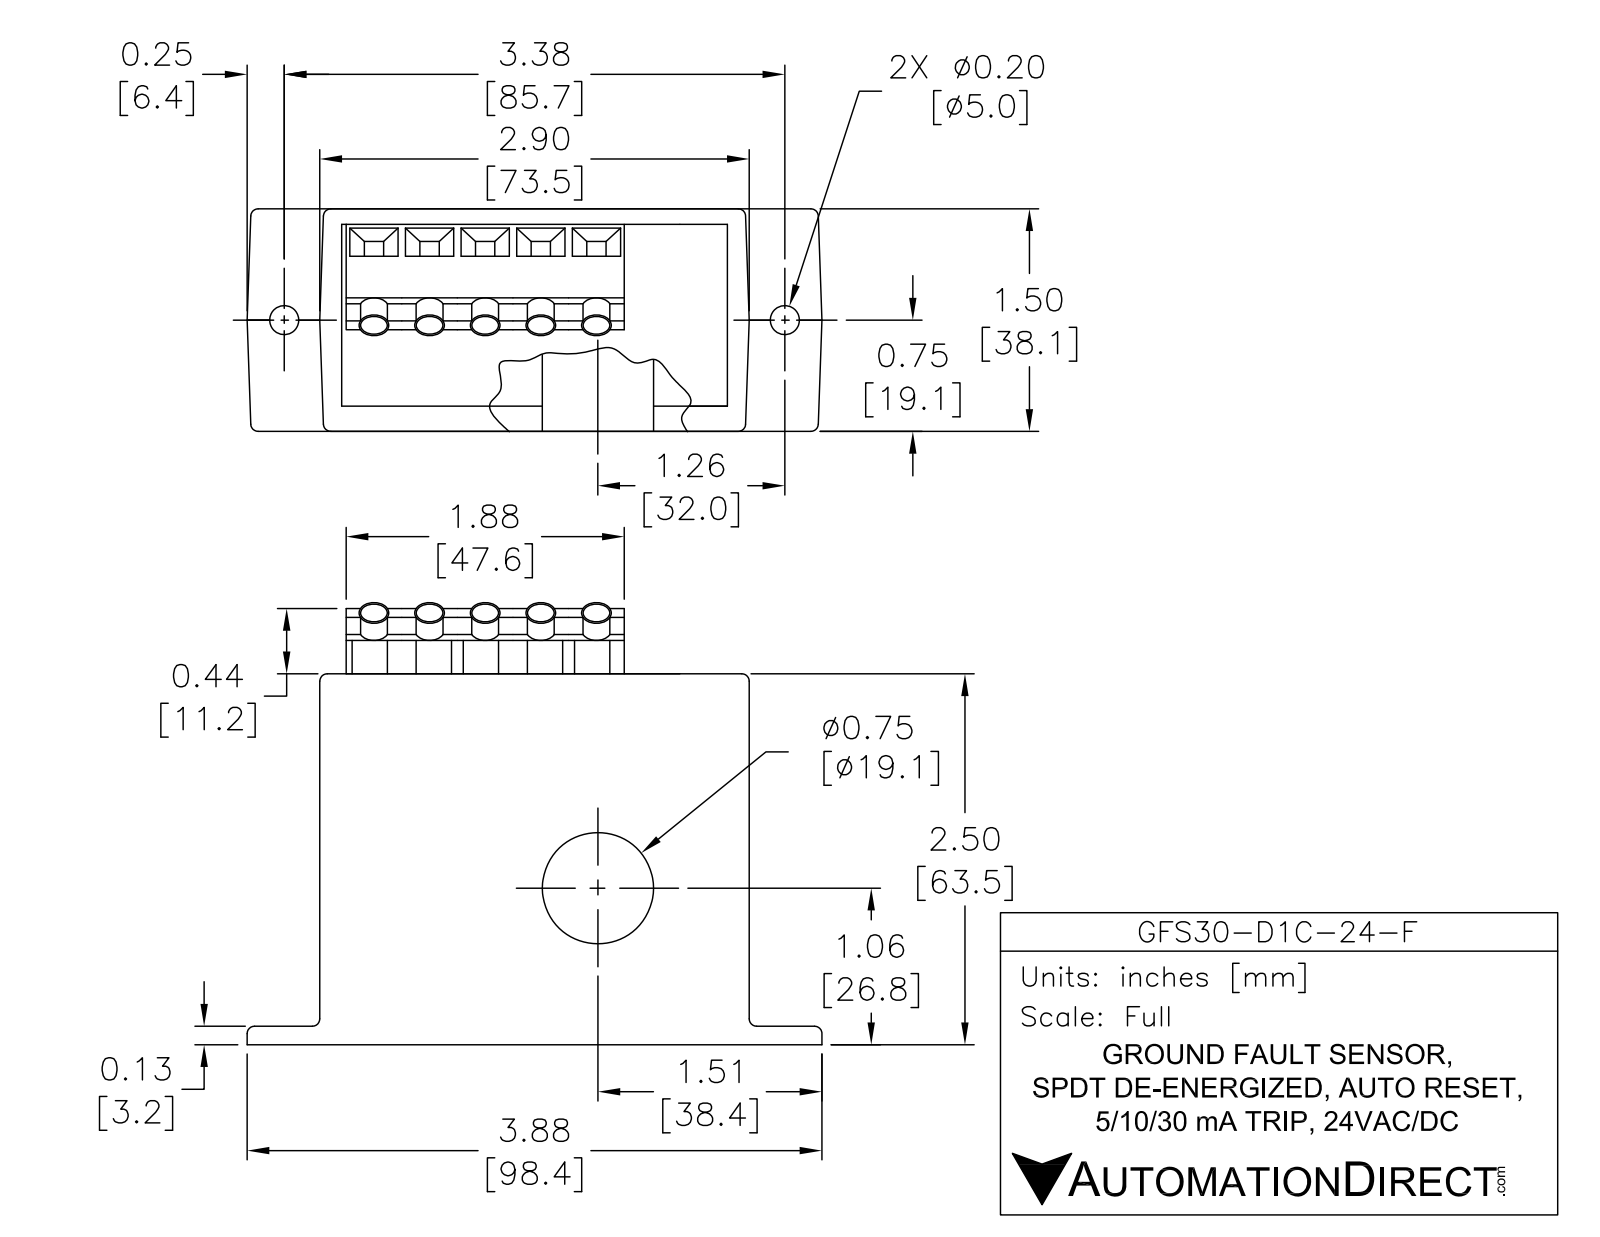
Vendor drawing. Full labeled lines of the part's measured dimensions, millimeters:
Part name (STEP PRODUCT): GFS30-D1C-24-F
STEP written by: SolidWorks 2019 (AUTOMOTIVE_DESIGN)
Units: millimetres
Bodies: 20 solids, 318 faces (265 planar, 49 cylindrical, 4 other)
Overall size (bounding box): 98.4 × 73.9 × 38.2
Volume: 172 400 mm³ · Surface area: 34 610 mm²
Round holes (diameter × count): ⌀5.2 ×5, ⌀5 ×2, ⌀5.1 ×2, ⌀19.1 ×1
Round bosses / shafts (diameter × count): ⌀4.7 ×5
Partial cylindrical surfaces — rounded edges, fillets, slot ends (radius × count): R3.3 ×5
Main face-to-face distances: 38.1, 62.4, 73.5, 2.5, 59.8, 38.2, 2.6, 62.5, 1.1, 3.2
Hole centre spacings: 19, 9, 10, 9.4, 17.3, 26, 28, 29
